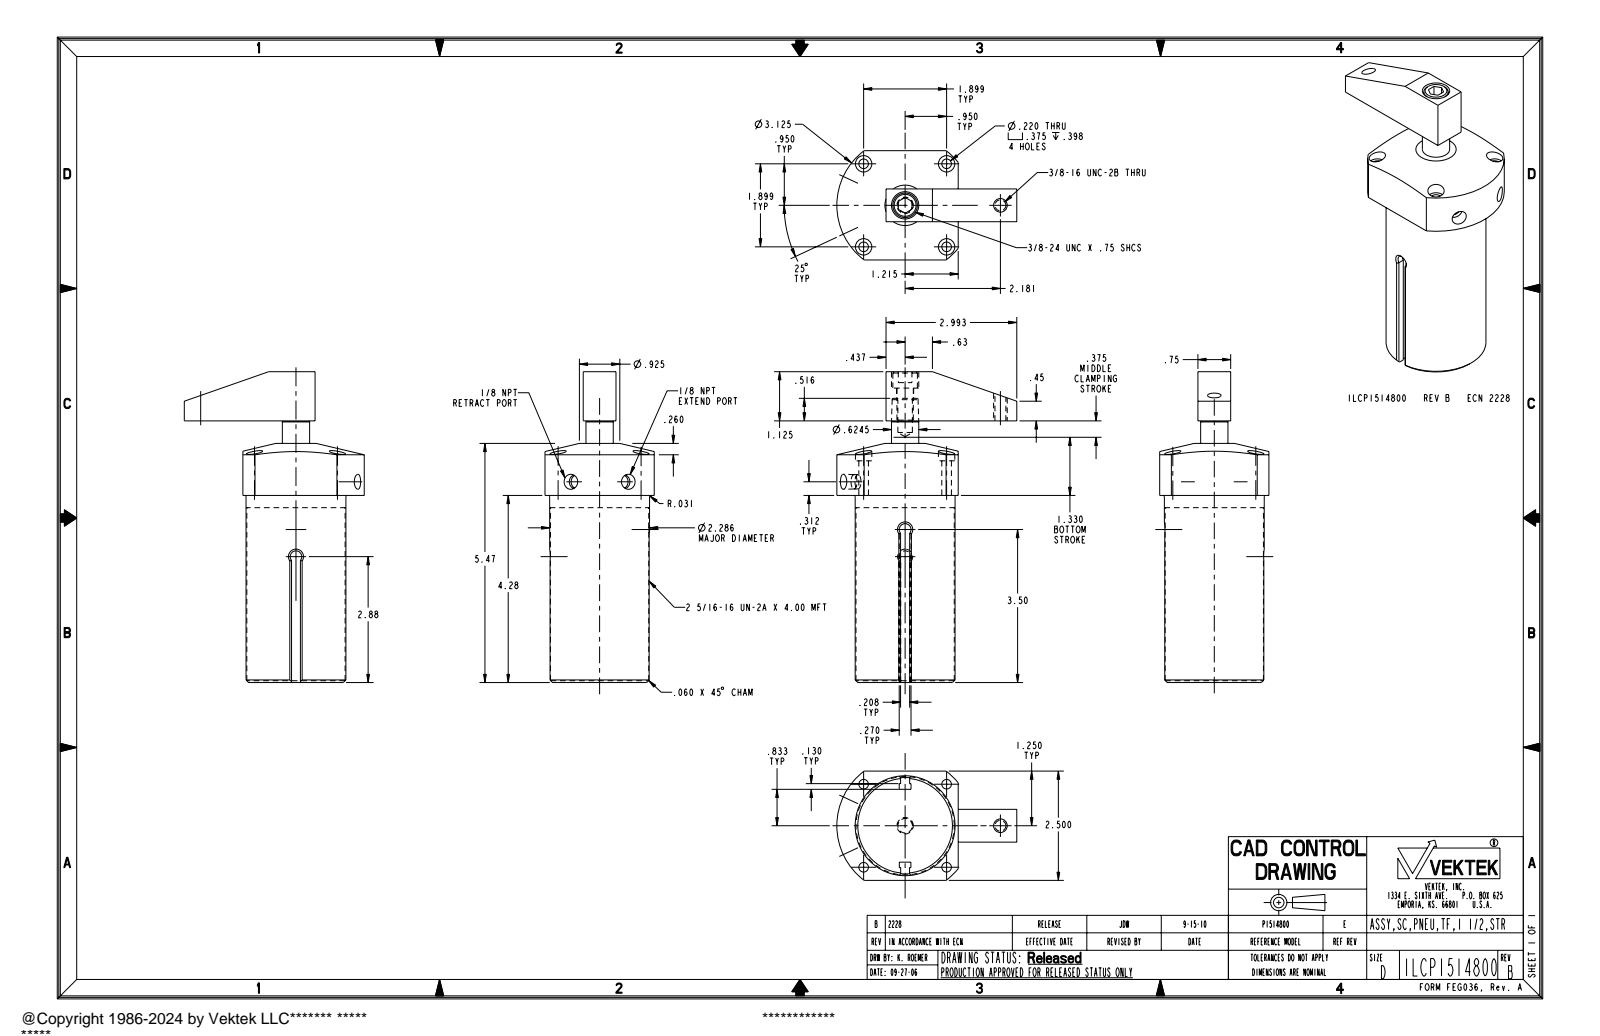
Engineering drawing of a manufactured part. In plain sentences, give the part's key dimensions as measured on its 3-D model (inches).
The part is named "ILCP1514800; ILC91501503; ILCP1514800_ASM". Its 3-D file was written by "PRO/ENGINEER BY PARAMETRIC TECHNOLOGY CORPORATION, 2007460 (AUTOMOTIVE_DESIGN_CC2)". It is 2 solids with 123 faces: 52 planar, 47 cylindrical and 24 other. Overall it measures 7.11 by 4.119 by 2.5 inches. Its volume is 25.67 cubic inches and its surface area 107.2 square inches. Round holes: 4 of diameter 0.22, 4 of diameter 0.375, 2 of diameter 0.328, 1 of diameter 0.312, 1 of diameter 0.332, 1 of diameter 0.39, 1 of diameter 0.625. Round bosses or shafts: 1 of diameter 2.286, 1 of diameter 2.25, 1 of diameter 0.624, 1 of diameter 0.562, 1 of diameter 0.375, 1 of diameter 0.25. Partial cylindrical surfaces (rounded edges, fillets, slot ends): 1 of radius 0.132, 1 of radius 0.135, 1 of radius 1.563. The main face-to-face distances are 0.875, 1.625, 0.75, 4.28, 1.705, 5.985, 2.5, 0.417, 2.083, 0.458. The hole center spacings are 1.343, 1.899, 1.555, 2.686, 3.272, 2.181.
